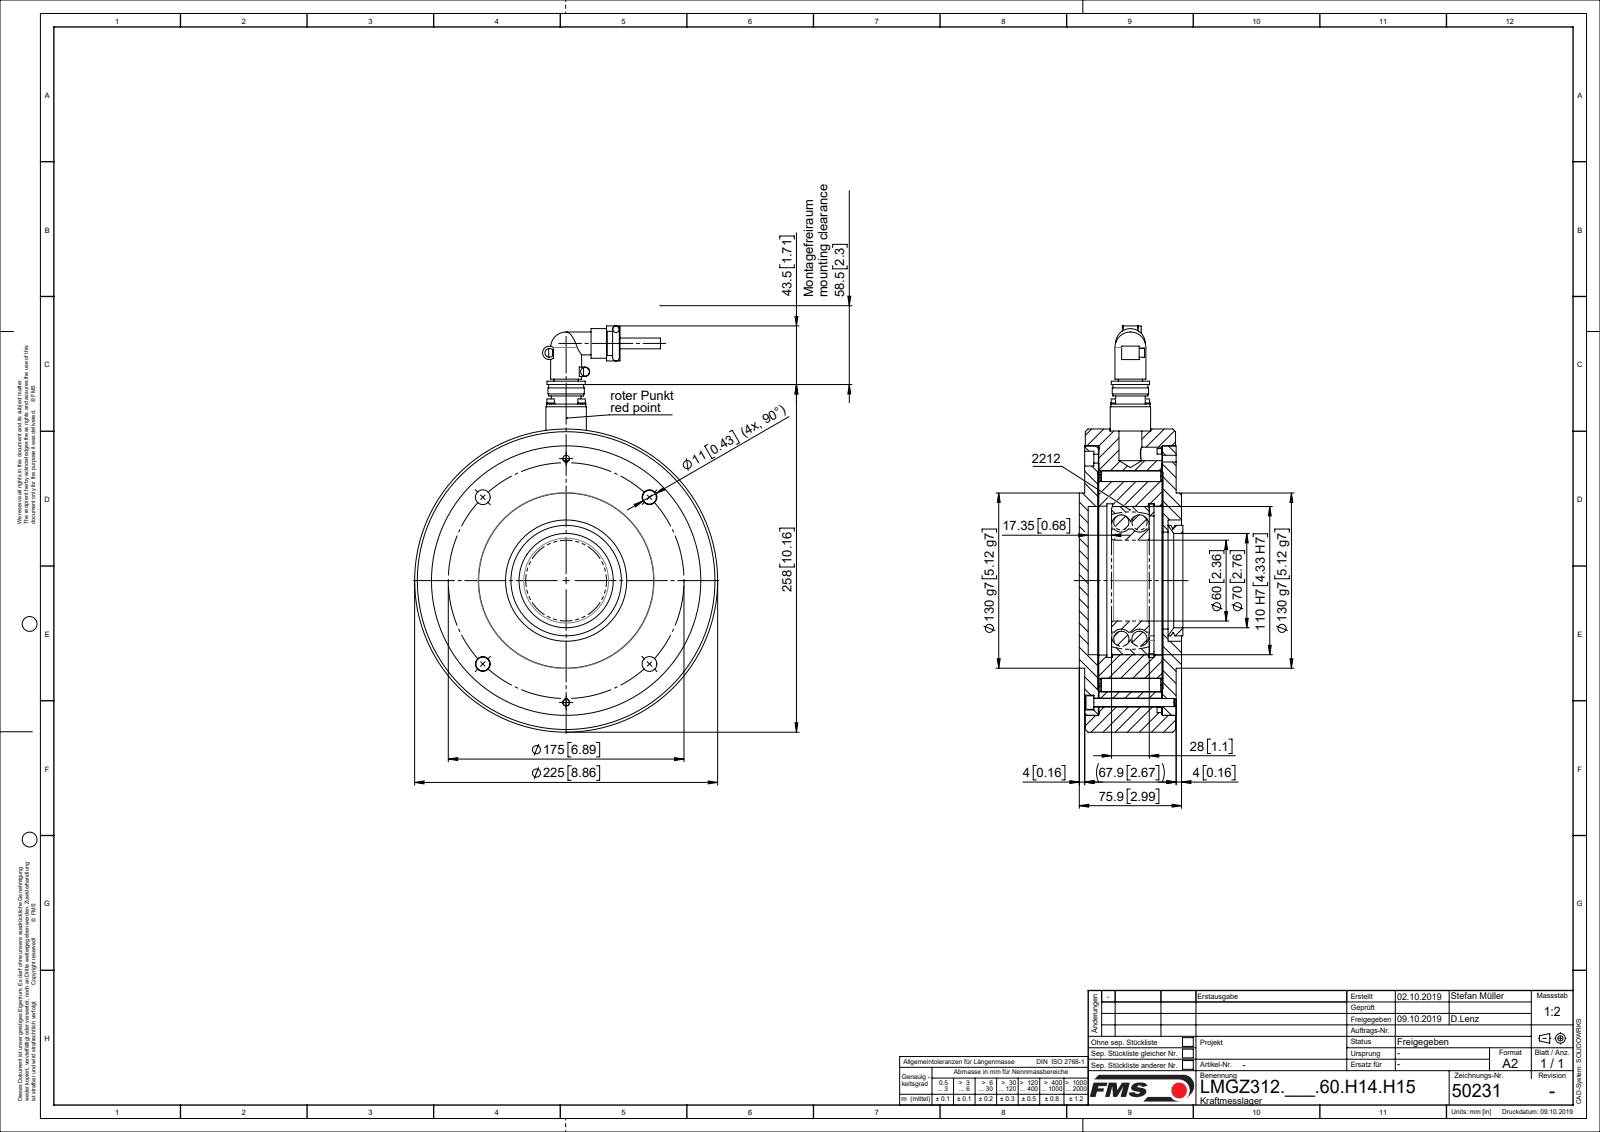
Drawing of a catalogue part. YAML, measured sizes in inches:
part_name: "ZEICHNUNG7; L50231; L49151; TEIL1 (+8 more)"
step_written_by: "Mechanical Desktop 2007 (CONFIG_CONTROL_DESIGN)"
units: inches
bodies: {solids: 19, faces: 391, planar: 118, cylindrical: 224, other: 49}
overall_size: [11.87, 8.858, 3.028]
volume: 145.7
surface_area: 606.7
round_holes:
  - {diameter: 0.433, count: 6}
  - {diameter: 0.102, count: 4}
  - {diameter: 0.126, count: 4}
  - {diameter: 0.134, count: 4}
  - {diameter: 0.138, count: 4}
  - {diameter: 0.354, count: 4}
  - {diameter: 0.197, count: 2}
  - {diameter: 0.26, count: 2}
  - {diameter: 0.906, count: 1}
  - {diameter: 2.362, count: 1}
  - {diameter: 2.756, count: 1}
  - {diameter: 2.835, count: 1}
round_bosses_or_shafts:
  - {diameter: 0.244, count: 4}
  - {diameter: 0.217, count: 4}
  - {diameter: 0.118, count: 4}
  - {diameter: 0.866, count: 2}
  - {diameter: 0.256, count: 2}
  - {diameter: 0.189, count: 2}
  - {diameter: 8.858, count: 1}
  - {diameter: 7.835, count: 1}
partial_cylinders:
  - {radius: 0.098, count: 2}
  - {radius: 0.138, count: 1}
  - {radius: 0.197, count: 1}
  - {radius: 3.189, count: 1}
  - {radius: 3.386, count: 1}
face_to_face_distances: [1.86, 0.411, 0.402, 2.262, 2.272, 1.87, 0.384, 0.02, 1.89, 0.382]
hole_center_spacings: [0.64, 0.906, 2.684, 3.445, 4.872, 6.474, 1.281, 3.563]
